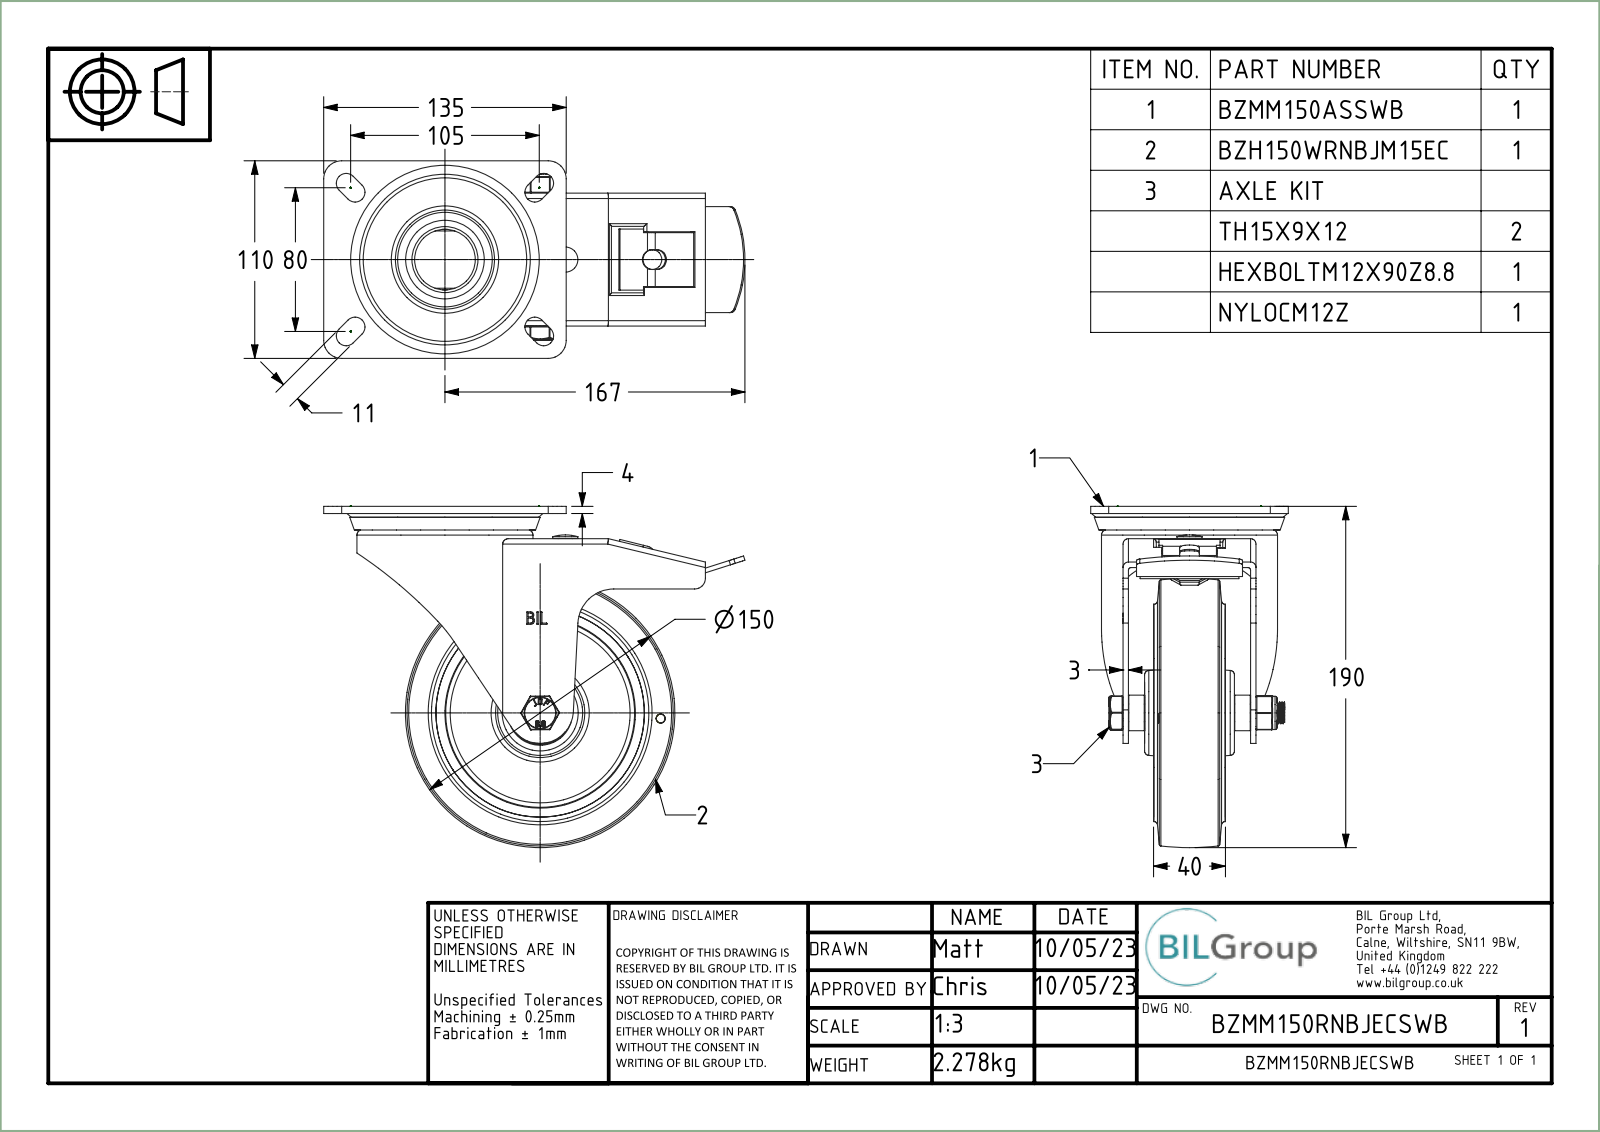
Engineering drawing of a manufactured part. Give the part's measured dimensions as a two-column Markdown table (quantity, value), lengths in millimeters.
| quantity | value |
| --- | --- |
| part name | ZINC PLATED, PRESSED STEEL TOP PLATE; ZINC PLATED, PRESSED STEEL TOP PLATE Geometry; BALL BEARINGS; BZMM150ASSWB - 68 (+7 more) |
| STEP written by | Spatial InterOp 3D (CONFIG_CONTROL_DESIGN) |
| units | millimeters |
| bodies | 83 solids, 1613 faces (529 planar, 435 cylindrical, 649 other) |
| overall size | 234.5 × 190 × 110 |
| volume | 639 366 mm³ |
| surface area | 275 862 mm² |
| round holes (diameter × count) | 5 × 1, 8 × 1, 11 × 1, 12 × 1, 12.2 × 1, 12.5 × 1, 14 × 1, 15 × 1, 20 × 1, 22.5 × 1, 30 × 1, 31 × 1 |
| round bosses / shafts (diameter × count) | 121 × 1, 98 × 1, 78 × 1, 50 × 1, 30.5 × 1, 23 × 1, 19.8 × 1, 18.5 × 1 |
| partial cylindrical surfaces (radius × count) | 0.5 × 24, 1.5 × 10, 5.5 × 10, 0.25 × 6, 2.5 × 6, 3 × 6, 0.47 × 4, 0.9 × 4 |
| main face-to-face distances | 3, 5, 9, 12, 4, 34.5, 39.5, 71, 17, 31.5 |
| hole center spacings | 67 |
